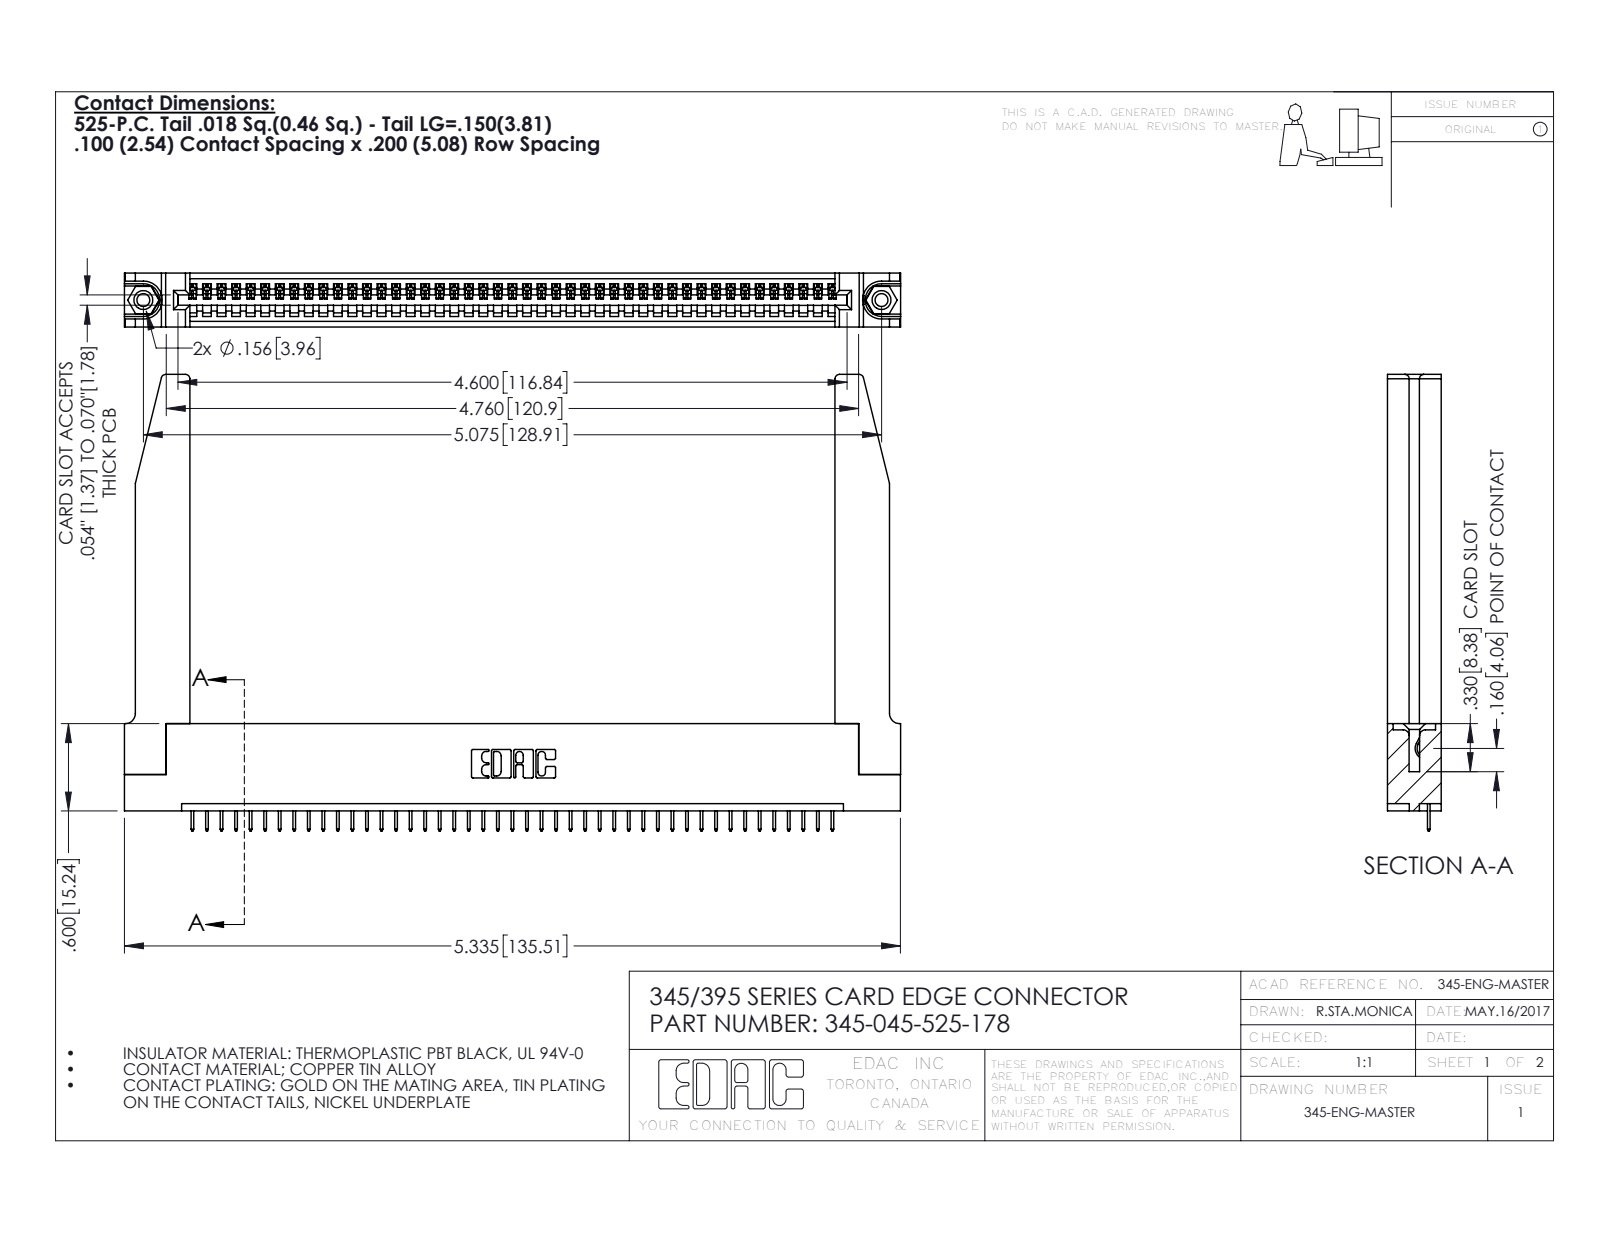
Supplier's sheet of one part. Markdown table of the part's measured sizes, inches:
| quantity | value |
| --- | --- |
| part name | 345-250-001_345-250-001-102; 345 Part_Flush Mounting Lugs - 0.156 Dia-TH; 345-292-001_345-293-125; 345-220-078_345-220-078 (+1 more) |
| STEP written by | SolidWorks 2020 (CONFIG_CONTROL_DESIGN) |
| units | inches |
| bodies | 50 solids, 3150 faces (2292 planar, 806 cylindrical, 52 other) |
| overall size | 5.336 × 3.137 × 0.37 |
| volume | 1.25 in³ |
| surface area | 35.91 in² |
| round holes (diameter × count) | 0.089 × 2, 0.125 × 2, 0.156 × 2, 0.064 × 1 |
| round bosses / shafts (diameter × count) | 0.155 × 2 |
| partial cylindrical surfaces (radius × count) | 0.006 × 90, 0.01 × 22, 0.03 × 8, 0.007 × 6, 0.031 × 6, 0.026 × 3, 0.031 × 2, 0.04 × 2 |
| main face-to-face distances | 0.37, 0.072, 0.298, 0.2, 0.098, 0.272, 0.025, 0.225, 0.148, 0.15 |
| hole center spacings | 0.27, 4.839, 5.075 |
